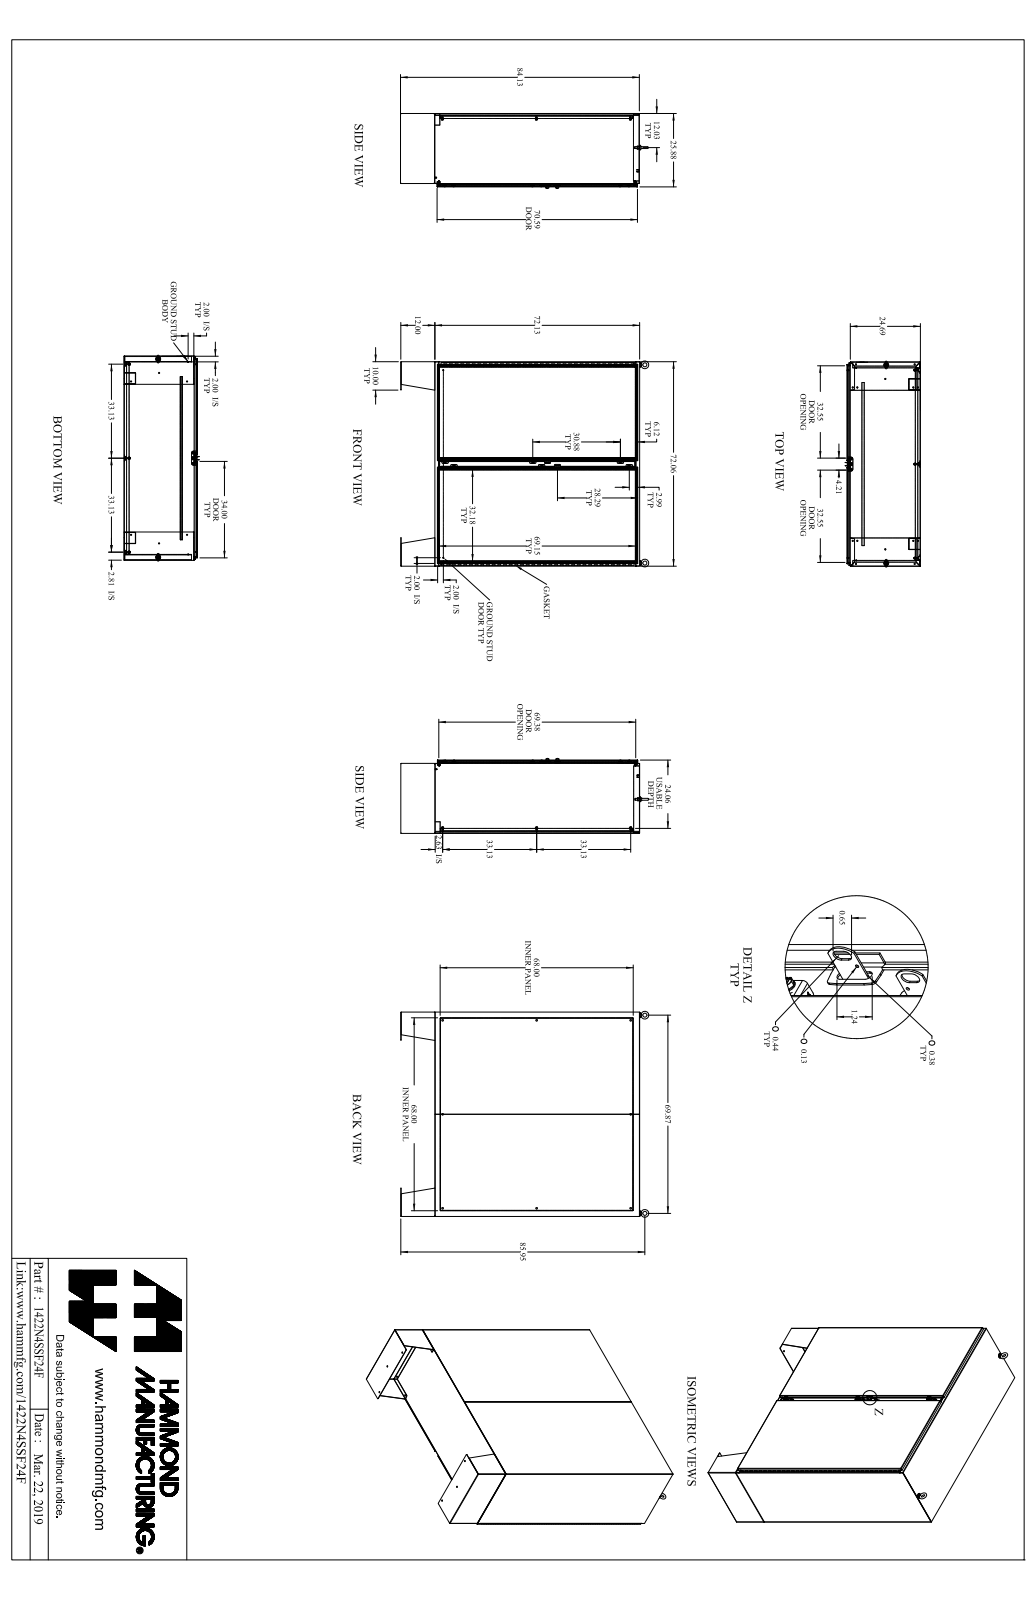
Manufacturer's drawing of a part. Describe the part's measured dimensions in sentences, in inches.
The part is named "1422N4SSF24F_Default". Its 3-D file was written by "SolidWorks 2019 (CONFIG_CONTROL_DESIGN)". It is 108 solids with 3630 faces: 1848 planar, 1586 cylindrical and 196 other. Overall it measures 87.784 by 73.121 by 26.468 inches. Its volume is 2 694 cubic inches and its surface area 54 312 square inches. Round holes: 24 of diameter 0.304, 14 of diameter 0.437, 8 of diameter 0.307, 8 of diameter 0.563, 6 of diameter 0.213, 6 of diameter 0.265, 6 of diameter 0.375, 6 of diameter 0.445, 3 of diameter 0.201, 3 of diameter 0.25, 3 of diameter 0.313, 2 of diameter 0.11. Round bosses or shafts: 8 of diameter 1, 8 of diameter 0.65, 8 of diameter 0.375, 8 of diameter 0.332, 6 of diameter 0.5, 6 of diameter 0.39, 6 of diameter 0.244, 4 of diameter 0.313. Partial cylindrical surfaces (rounded edges, fillets, slot ends): 69 of radius 0.048, 69 of radius 0.143, 34 of radius 0.25, 18 of radius 0.06, 12 of radius 0.116, 12 of radius 0.141, 12 of radius 0.185, 9 of radius 0.187. The main face-to-face distances are 0.095, 25.78, 25.685, 25.875, 0.125, 23.998, 24.093, 1.687, 1.782, 24.218. The hole center spacings are 6, 70.461, 12, 71.223, 72.476, 18, 24, 74.194.
